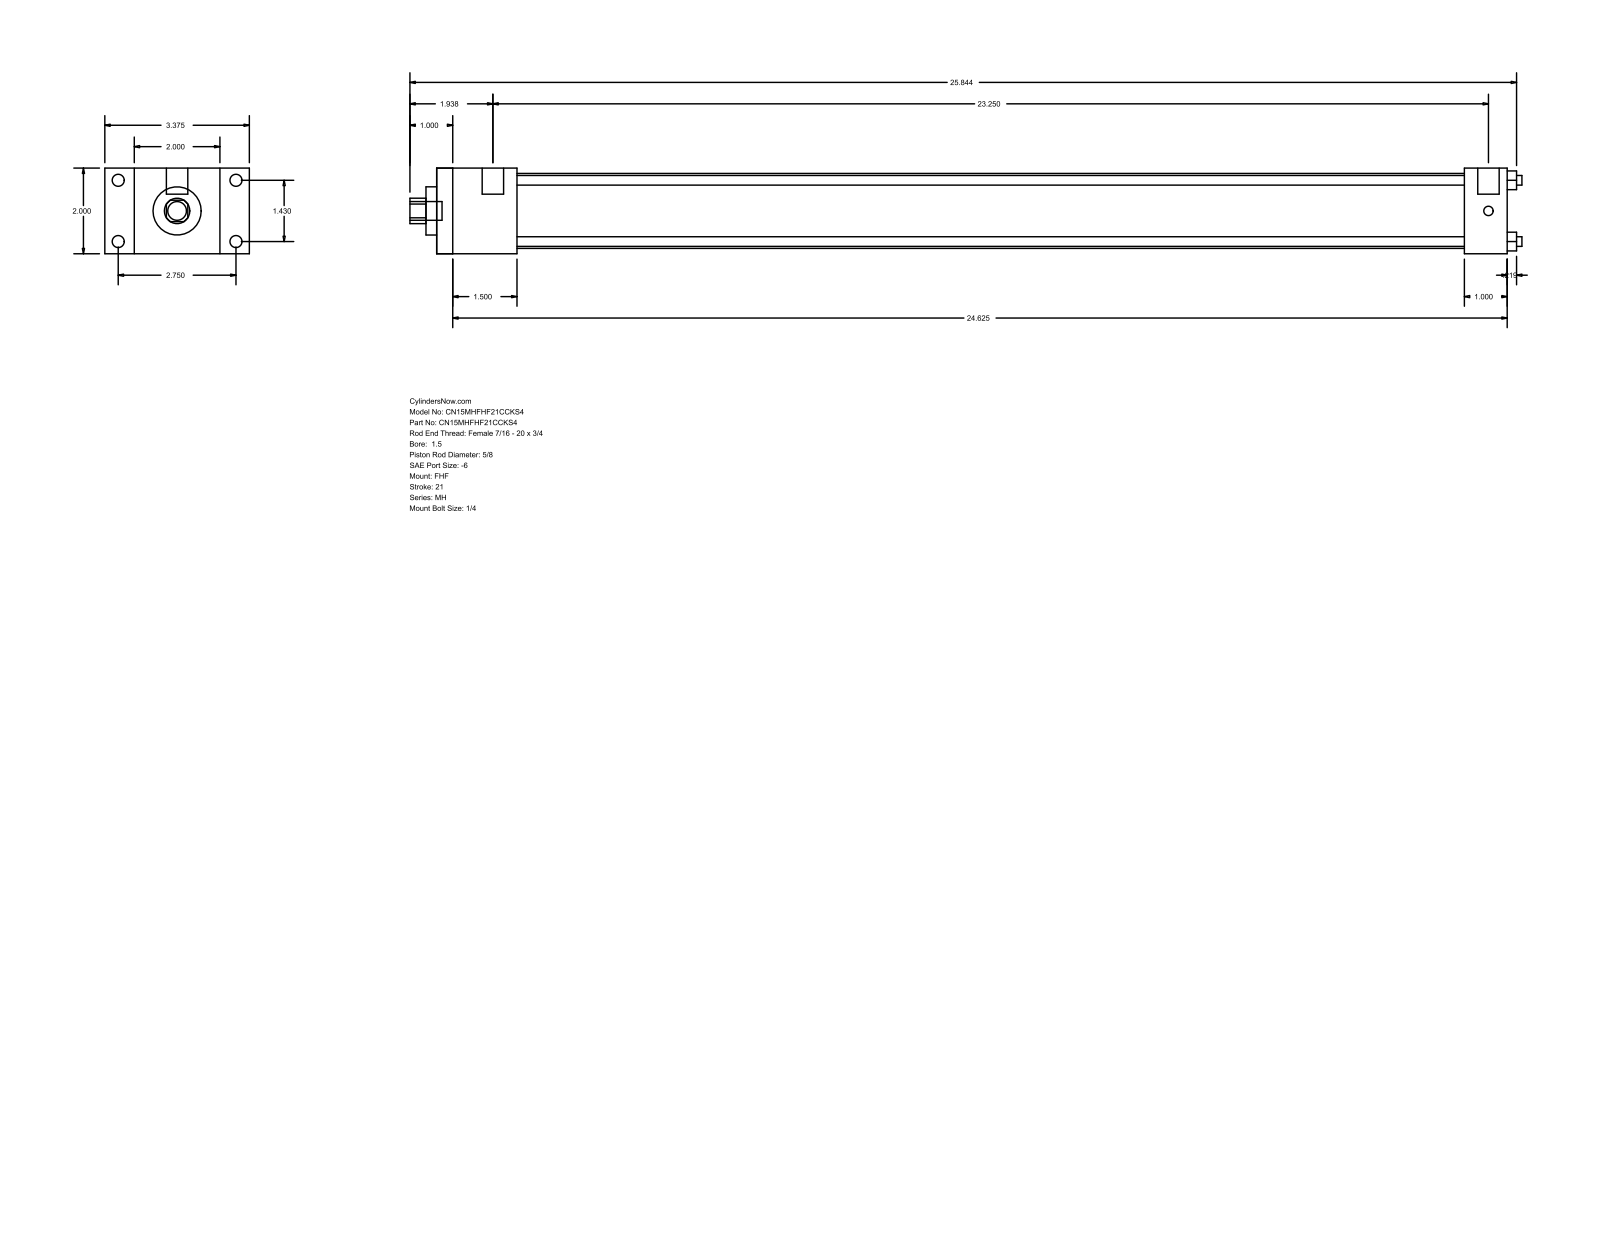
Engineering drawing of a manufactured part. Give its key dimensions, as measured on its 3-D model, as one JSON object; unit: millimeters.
{"part_name": "MH_FHF__0150_0.625", "step_written_by": "GSSL Pune (CONFIG_CONTROL_DESIGN)", "units": "millimeters", "bodies": {"solids": 0, "faces": 88, "planar": 60, "cylindrical": 28, "other": 0}, "overall_size": [659.61, 85.72, 50.8], "round_holes": [[5.71, 4], [15.88, 1], [28.57, 1], [44.45, 1]], "round_bosses_or_shafts": [[7.14, 4], [5.56, 4], [12.7, 2], [11.11, 1]], "partial_cylinders_radius": [[7.54, 1]], "face_to_face_distances": [50.8, 17.46, 68.26, 47.62, 85.72, 635, 587.38, 609.6, 561.98, 25.4], "hole_center_spacings": [25.68, 36.32, 51.36]}
